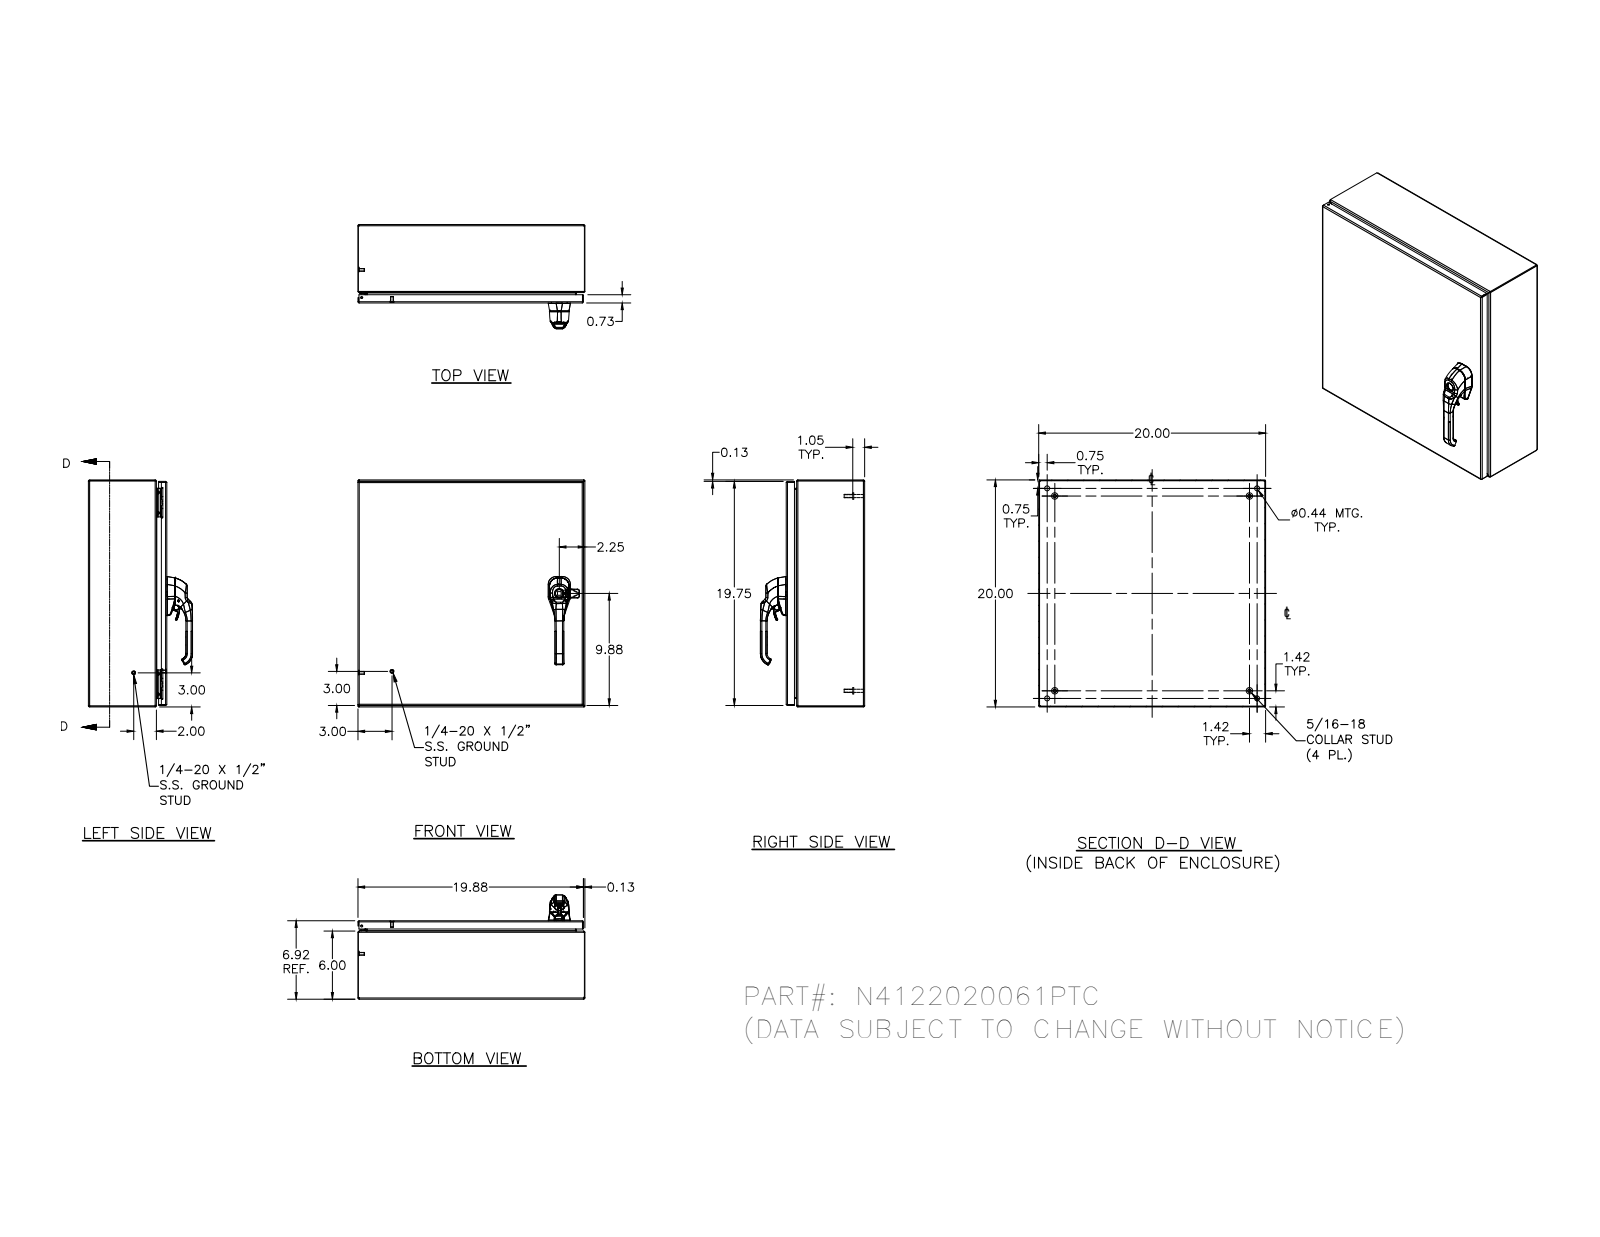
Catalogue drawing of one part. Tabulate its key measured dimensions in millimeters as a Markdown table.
| quantity | value |
| --- | --- |
| part name | N4122020061PTC |
| STEP written by | SolidWorks 2018 (AUTOMOTIVE_DESIGN) |
| units | millimeters |
| bodies | 28 solids, 1280 faces (417 planar, 474 cylindrical, 389 other) |
| overall size | 508 × 508 × 231 |
| volume | 1 904 000 mm³ |
| surface area | 1 894 000 mm² |
| round holes (diameter × count) | 4.8 × 5, 2.4 × 4, 3.9 × 4, 4.2 × 4, 4.4 × 4, 11.1 × 4, 7.1 × 3, 4 × 2, 4.7 × 1 |
| round bosses / shafts (diameter × count) | 6.4 × 10, 14.3 × 4, 9.1 × 4, 8.1 × 4, 7.6 × 4, 7 × 4, 6.5 × 4, 4.2 × 4 |
| partial cylindrical surfaces (radius × count) | 0.8 × 30, 1.3 × 26, 2.7 × 20, 0.4 × 18, 3.2 × 14, 0.8 × 8, 1.7 × 8, 1.7 × 8 |
| main face-to-face distances | 1.9, 173.8, 506.1, 175.7, 171.9, 504.2, 508, 150.5, 23.3, 18.8 |
| hole center spacings | 406.3, 469.9, 479.3, 0.4, 16.8, 406.5, 423.1, 0.5 |
